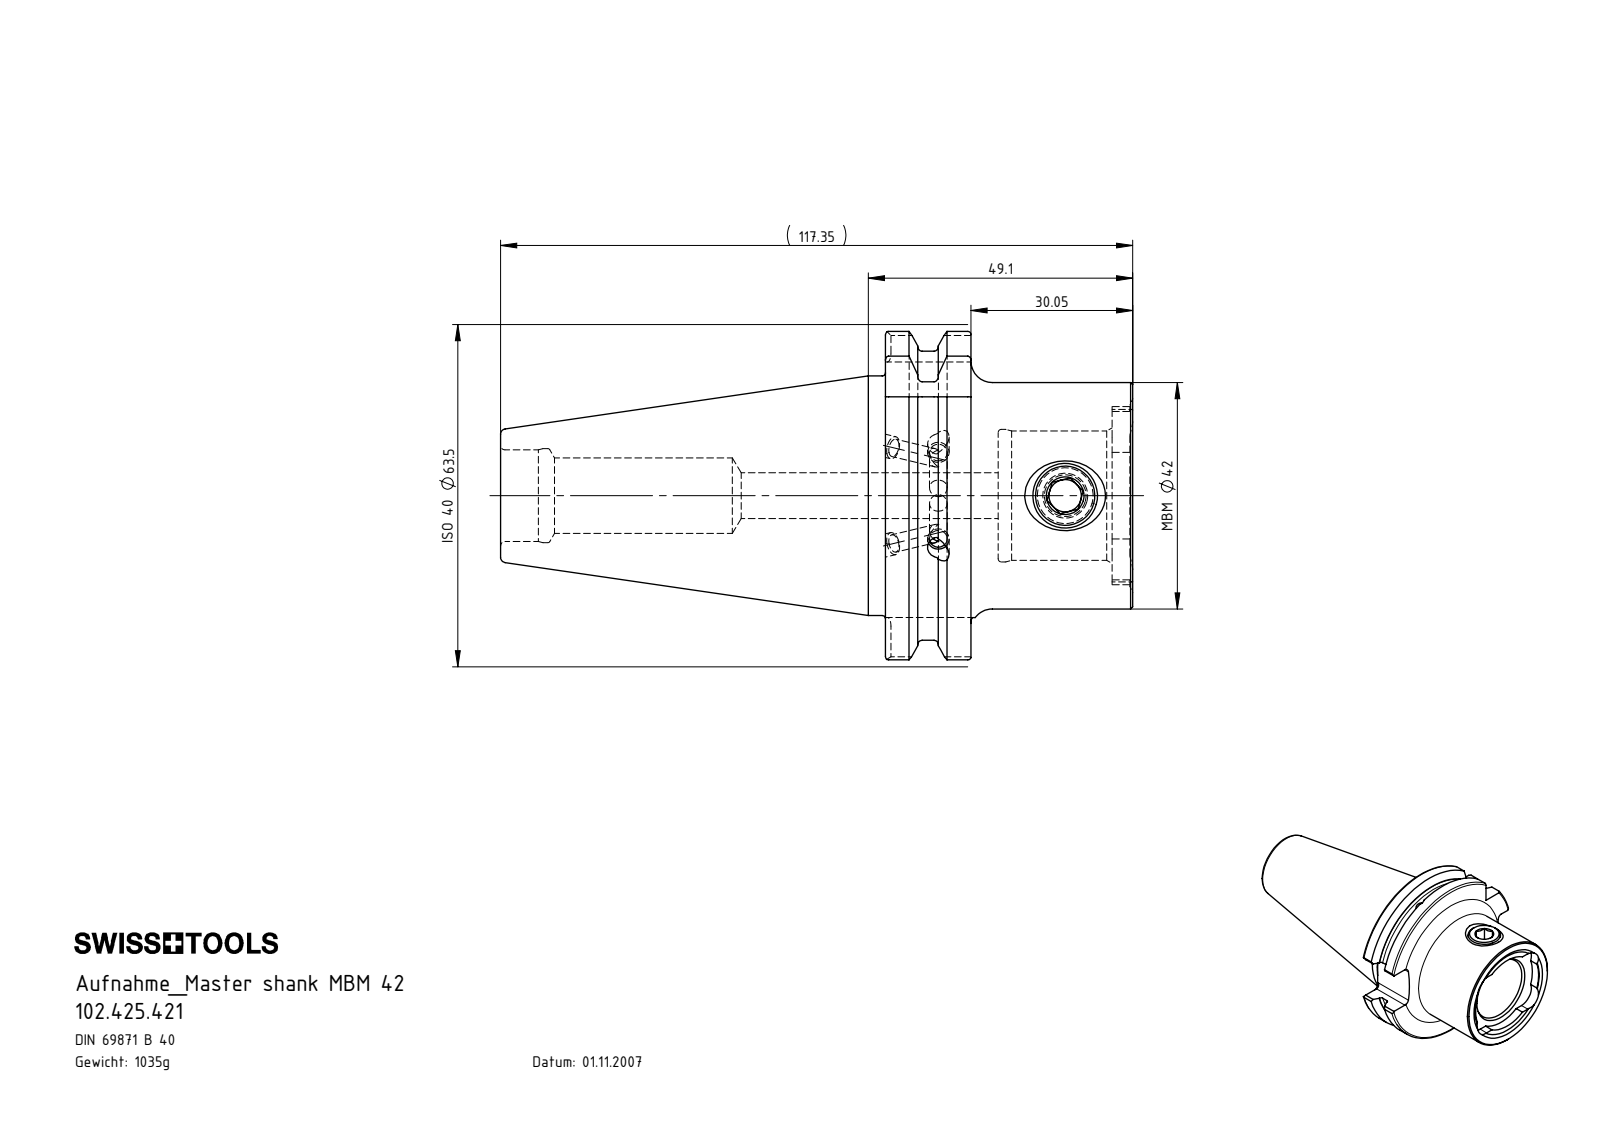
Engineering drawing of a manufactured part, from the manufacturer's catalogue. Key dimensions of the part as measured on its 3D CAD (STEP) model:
Part name (STEP PRODUCT): 102.425.421; MB4-ER1.001.013_A; SB4-MB4.K01.049_D_mit Bundkhlung
STEP written by: SolidWorks 2017 (CONFIG_CONTROL_DESIGN)
Units: millimetres
Bodies: 2 solids, 209 faces (58 planar, 72 cylindrical, 79 other)
Overall size (bounding box): 117.35 × 63.5 × 60.94
Volume: 131 847 mm³ · Surface area: 26 824 mm²
Round holes (diameter × count): ⌀3.3 ×3, ⌀4.2 ×2, ⌀4 ×1, ⌀6 ×1, ⌀8.5 ×1, ⌀11 ×1, ⌀14 ×1, ⌀17 ×1, ⌀17.45 ×1, ⌀24 ×1, ⌀24.6 ×1
Round bosses / shafts (diameter × count): ⌀44.45 ×1, ⌀42 ×1, ⌀12 ×1
Partial cylindrical surfaces — rounded edges, fillets, slot ends (radius × count): R1.6 ×8, R5.2 ×4, R14.9 ×1, R16.52 ×1, R28 ×1, R31.75 ×1
Main face-to-face distances: 15.85, 20.9, 5.05, 42.05, 26.2, 21.15, 3.85, 45.9, 30.05, 25
